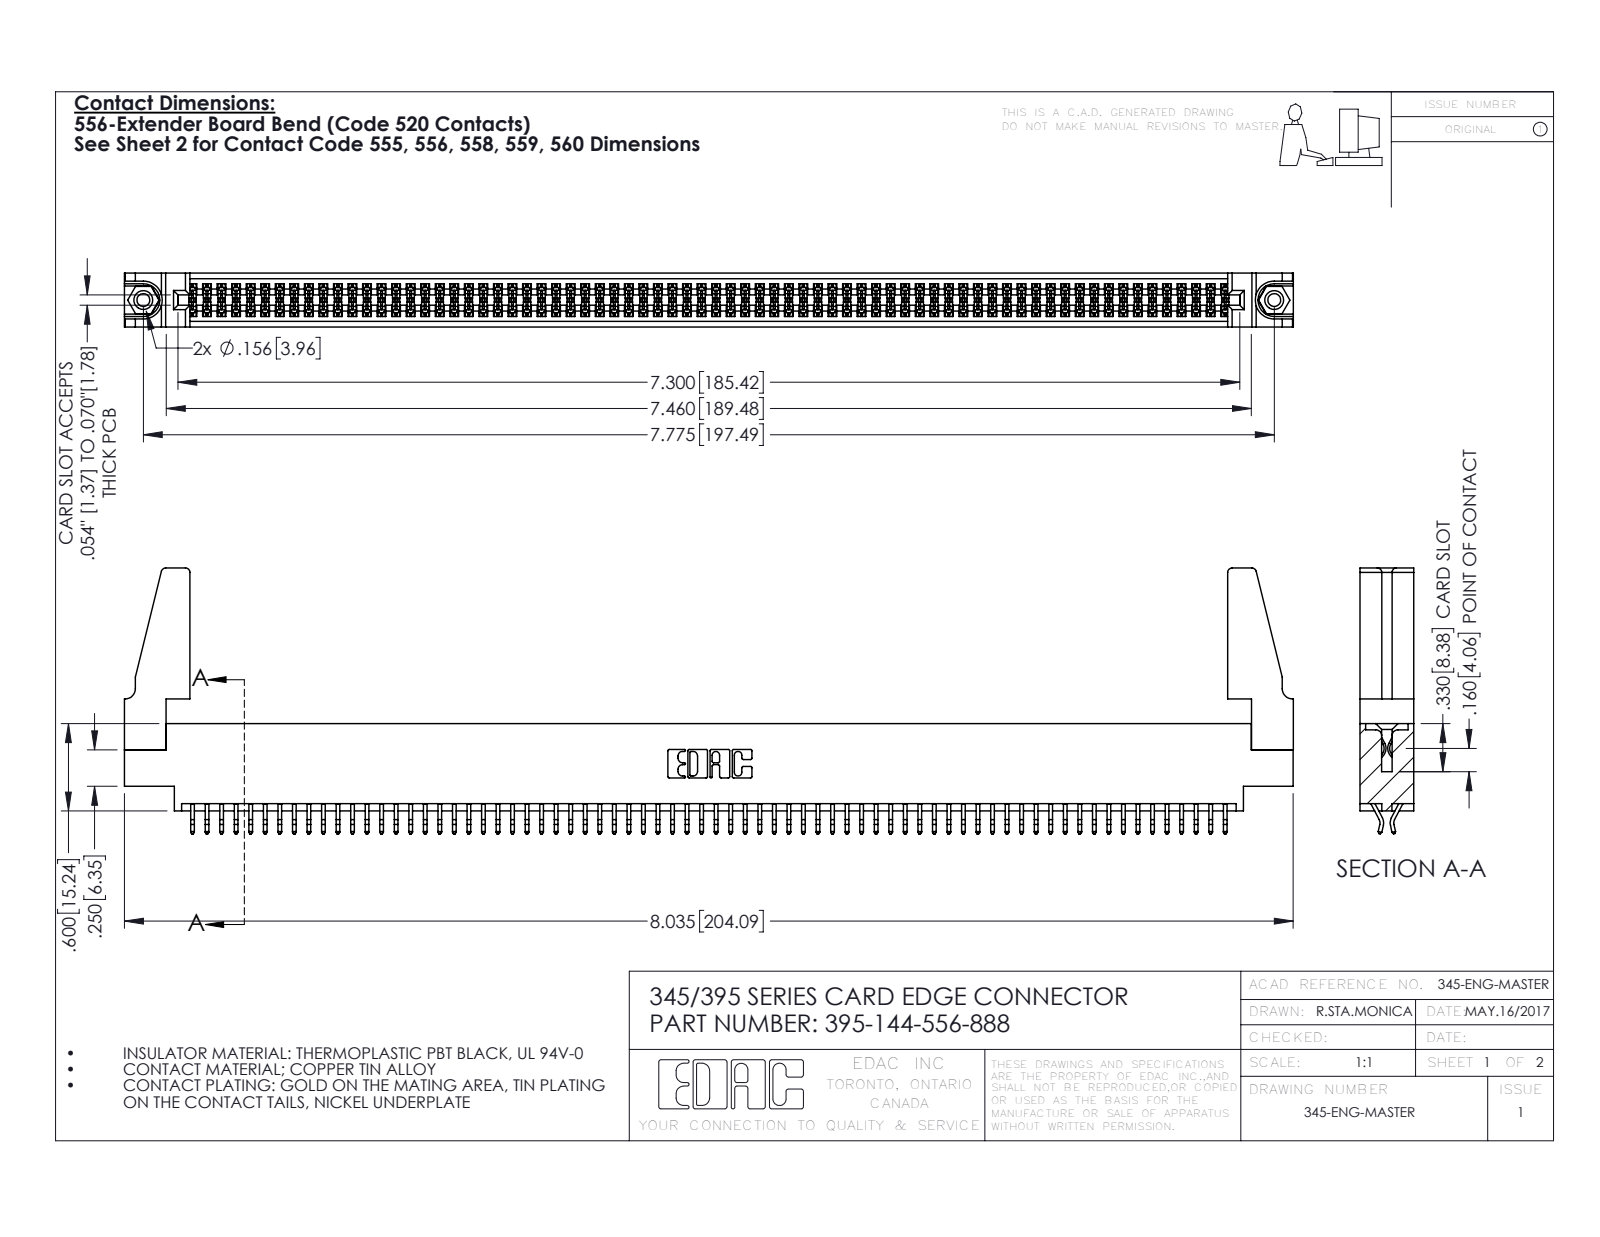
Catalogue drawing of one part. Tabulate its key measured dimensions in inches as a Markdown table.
| quantity | value |
| --- | --- |
| part name | 345 Part_0.170 Offset - 0.156 Dia-TH; 345-220-078_345-220-088; 345-292-001_556 Tail; 345-250-001_345-250-001-102 (+1 more) |
| STEP written by | SolidWorks 2016 (CONFIG_CONTROL_DESIGN) |
| units | inches |
| bodies | 149 solids, 8318 faces (5484 planar, 2818 cylindrical, 16 other) |
| overall size | 8.036 × 1.827 × 0.37 |
| volume | 1.418 in³ |
| surface area | 51.56 in² |
| round holes (diameter × count) | 0.089 × 2, 0.125 × 2, 0.156 × 2, 0.064 × 1 |
| round bosses / shafts (diameter × count) | 0.155 × 2 |
| partial cylindrical surfaces (radius × count) | 0.006 × 216, 0.01 × 22, 0.03 × 8, 0.007 × 6, 0.031 × 6, 0.026 × 3, 0.01 × 2, 0.014 × 2 |
| main face-to-face distances | 0.072, 0.298, 0.37, 0.025, 0.2, 0.098, 0.272, 0.225, 0.175, 0.149 |
| hole center spacings | 0.27, 7.539, 7.775 |
